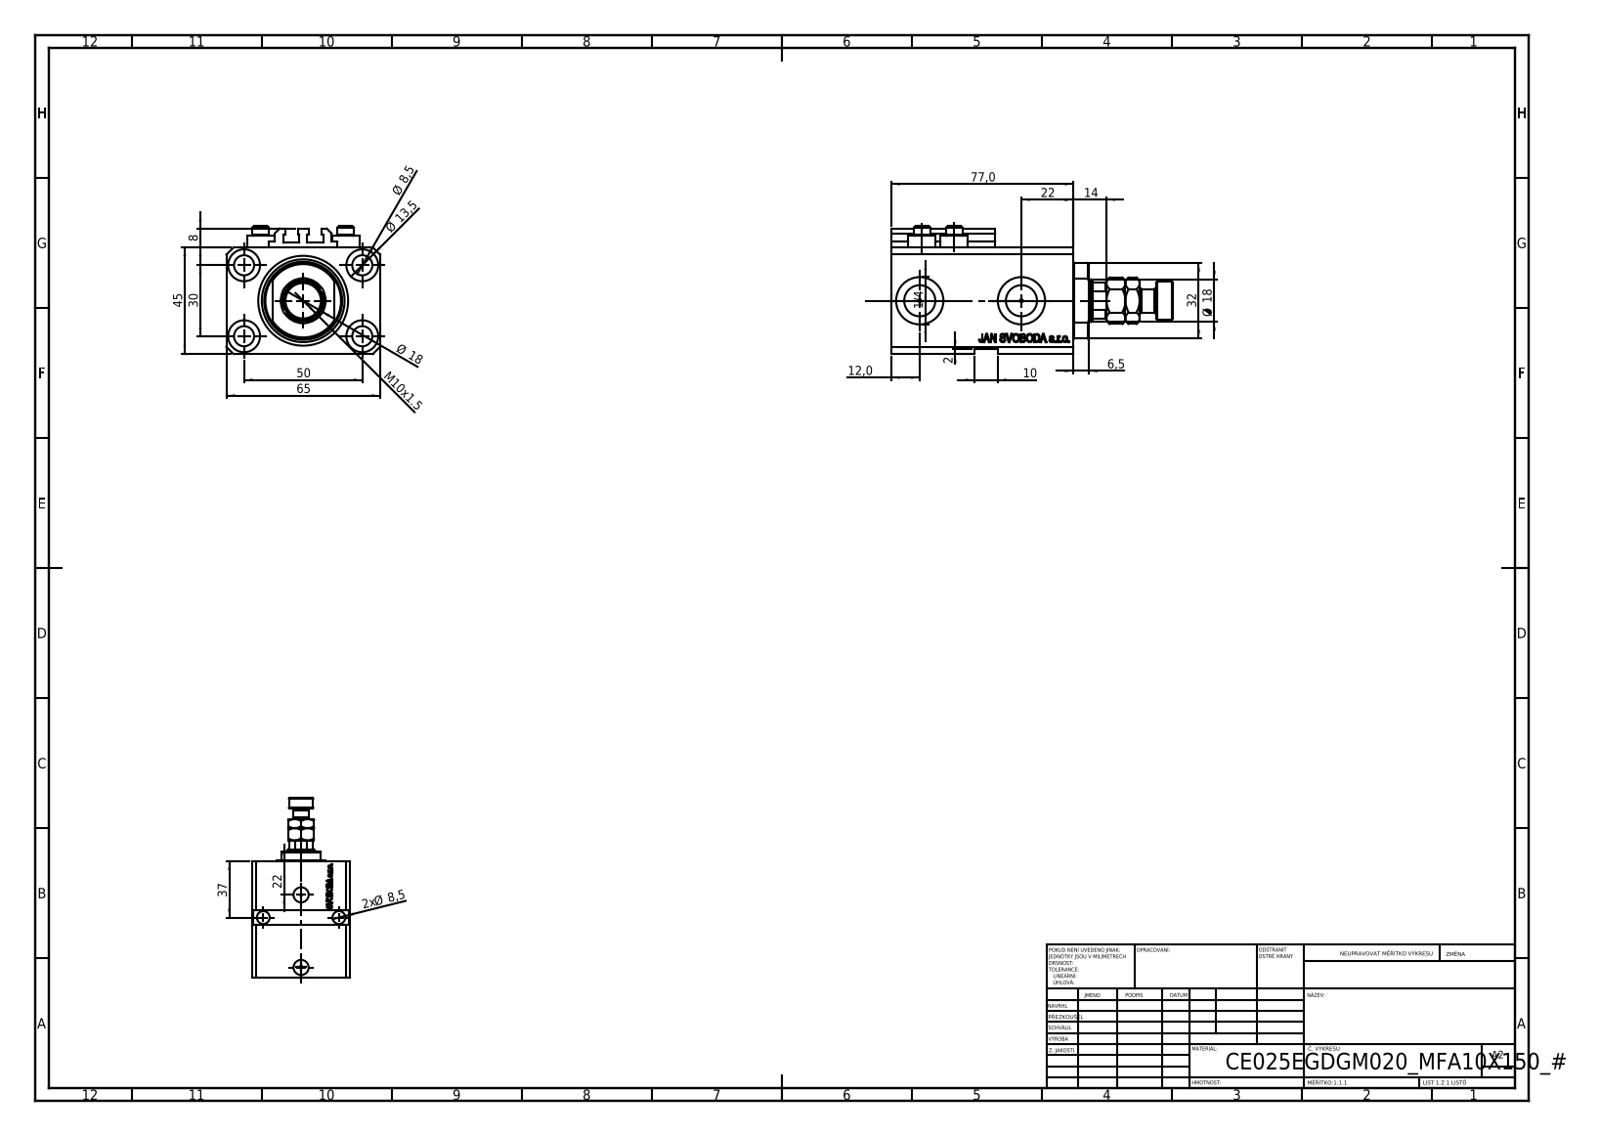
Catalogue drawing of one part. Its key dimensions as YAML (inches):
part_name: "V250CE_VC_E; V250CE_E_Body; MFA; ALLEN BOLT V250CE (+1 more)"
step_written_by: "SolidWorks 2019 (CONFIG_CONTROL_DESIGN)"
units: inches
bodies: {solids: 9, faces: 1135, planar: 531, cylindrical: 142, other: 462}
overall_size: [4.685, 2.559, 2.126]
volume: 12.3
surface_area: 96.7
round_holes:
  - {diameter: 0.335, count: 7}
  - {diameter: 0.049, count: 4}
  - {diameter: 0.157, count: 4}
  - {diameter: 0.531, count: 4}
  - {diameter: 0.394, count: 2}
  - {diameter: 0.518, count: 2}
  - {diameter: 0.787, count: 2}
  - {diameter: 0.709, count: 1}
  - {diameter: 0.984, count: 1}
  - {diameter: 1.496, count: 1}
round_bosses_or_shafts:
  - {diameter: 0.457, count: 4}
  - {diameter: 0.276, count: 4}
  - {diameter: 0.63, count: 1}
  - {diameter: 0.394, count: 1}
partial_cylinders:
  - {radius: 0.008, count: 10}
  - {radius: 0.335, count: 1}
  - {radius: 0.63, count: 1}
face_to_face_distances: [1.772, 2.559, 0.551, 2.48, 3.031, 0.079, 0.272, 2.209, 2.76, 0.807]
hole_center_spacings: [1.148, 1.969, 0.535, 0.595, 0.741, 0.747, 1.032, 1.048]
